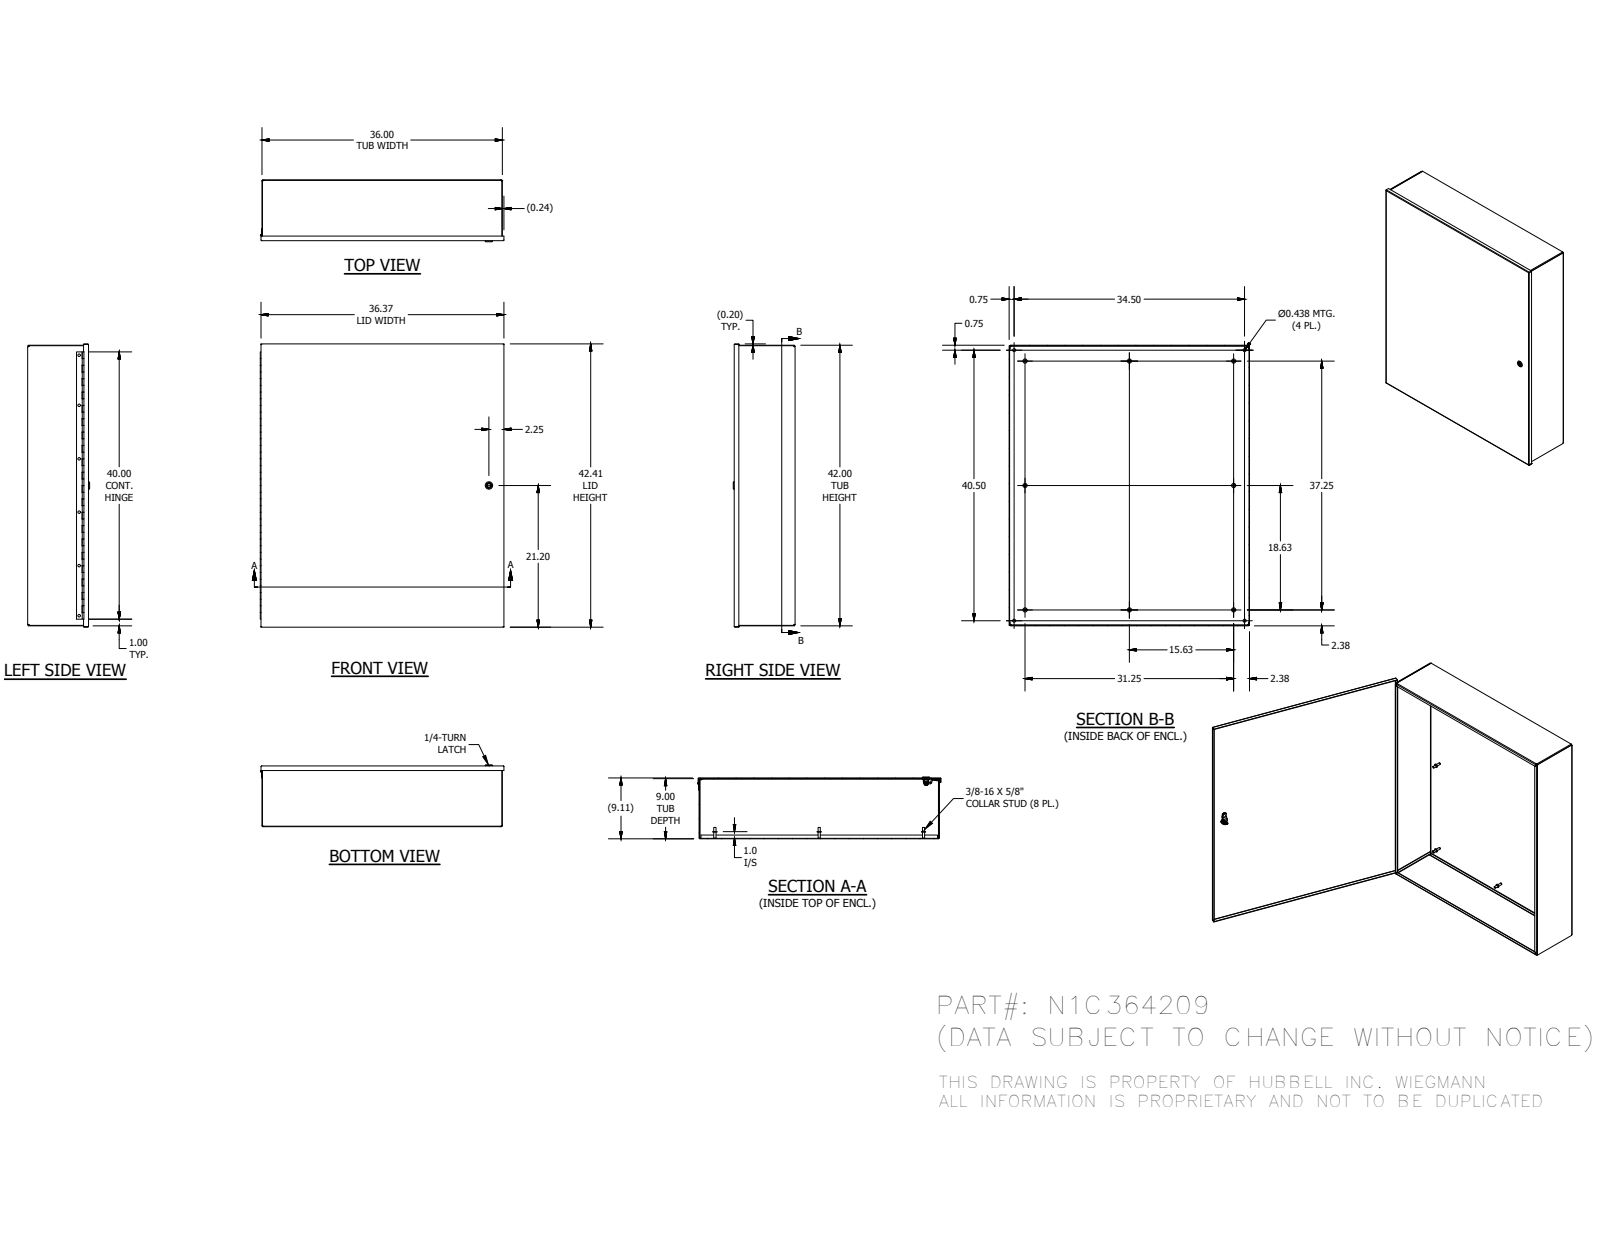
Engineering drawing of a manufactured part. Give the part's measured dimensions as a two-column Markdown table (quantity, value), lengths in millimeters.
| quantity | value |
| --- | --- |
| part name | N1C364209BLR; N1C3609TB; N1C3642LID; 1000-101-GPF_GPD (+8 more) |
| STEP written by | Autodesk Inventor 2016 (AUTOMOTIVE_DESIGN) |
| units | millimeters |
| bodies | 22 solids, 994 faces (645 planar, 279 cylindrical, 70 other) |
| overall size | 1077.12 × 926.81 × 235.27 |
| volume | 5 744 000 mm³ |
| surface area | 6 151 000 mm² |
| round holes (diameter × count) | 9.52 × 6, 11.11 × 4, 3.17 × 1, 5 × 1, 8 × 1, 10 × 1, 10.2 × 1, 16.1 × 1, 20.38 × 1 |
| round bosses / shafts (diameter × count) | 15.88 × 8, 8.38 × 8, 28 × 1, 27 × 1, 23 × 1, 19.8 × 1, 15.8 × 1, 15.2 × 1 |
| partial cylindrical surfaces (radius × count) | 0.3 × 30, 3.47 × 12, 1.59 × 11, 0.5 × 10, 0.79 × 4, 2.67 × 4, 4 × 4, 0.4 × 3 |
| main face-to-face distances | 1.88, 229.39, 227.51, 231.27, 912.52, 1064.92, 910.64, 914.4, 1063.04, 1066.8 |
| hole center spacings | 203.2, 190.5, 393.7, 406.4, 515.35, 596.9, 800.1, 876.3 |
